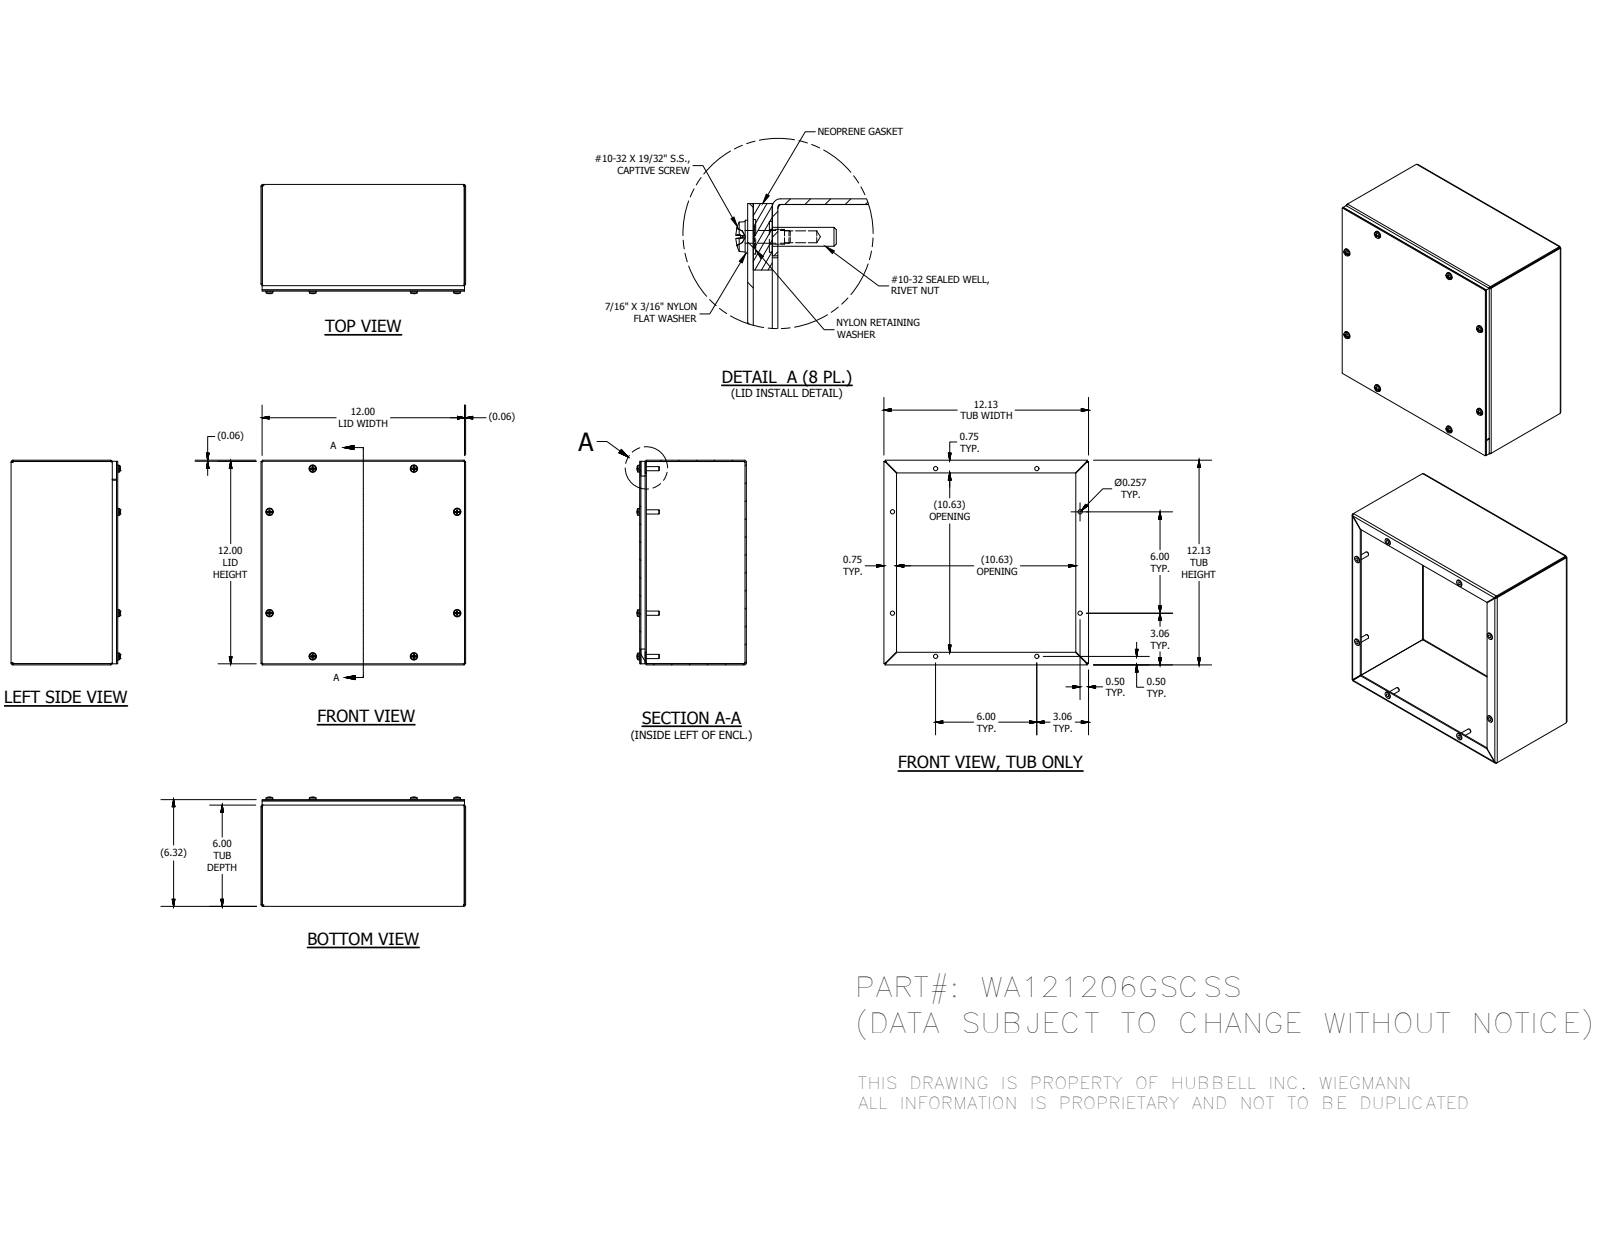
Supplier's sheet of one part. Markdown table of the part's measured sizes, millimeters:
| quantity | value |
| --- | --- |
| part name | WA121206GSCSSBKP; WA1212GSCSSLID; 316282; 37210 (+4 more) |
| STEP written by | Autodesk Inventor 2016 (AUTOMOTIVE_DESIGN) |
| units | millimeters |
| bodies | 36 solids, 764 faces (420 planar, 160 cylindrical, 184 other) |
| overall size | 307.98 × 307.98 × 164.56 |
| volume | 895 010 mm³ |
| surface area | 863 378 mm² |
| round holes (diameter × count) | 3.96 × 8, 4.78 × 8, 4.98 × 8, 6.53 × 8, 7.06 × 8, 7.14 × 8, 7.95 × 8 |
| round bosses / shafts (diameter × count) | 11.51 × 8, 11.11 × 8, 10.31 × 8, 6.3 × 8, 4.25 × 8 |
| partial cylindrical surfaces (radius × count) | 0.79 × 12, 1.78 × 8, 2.27 × 8, 2.67 × 8 |
| main face-to-face distances | 1.88, 158.75, 306.1, 160.63, 156.87, 307.98, 304.22, 150.52, 8.23, 6.35 |
| hole center spacings | 152.4, 227, 227.02, 92.04, 282.56, 307.56, 321.04, 92.02 |
